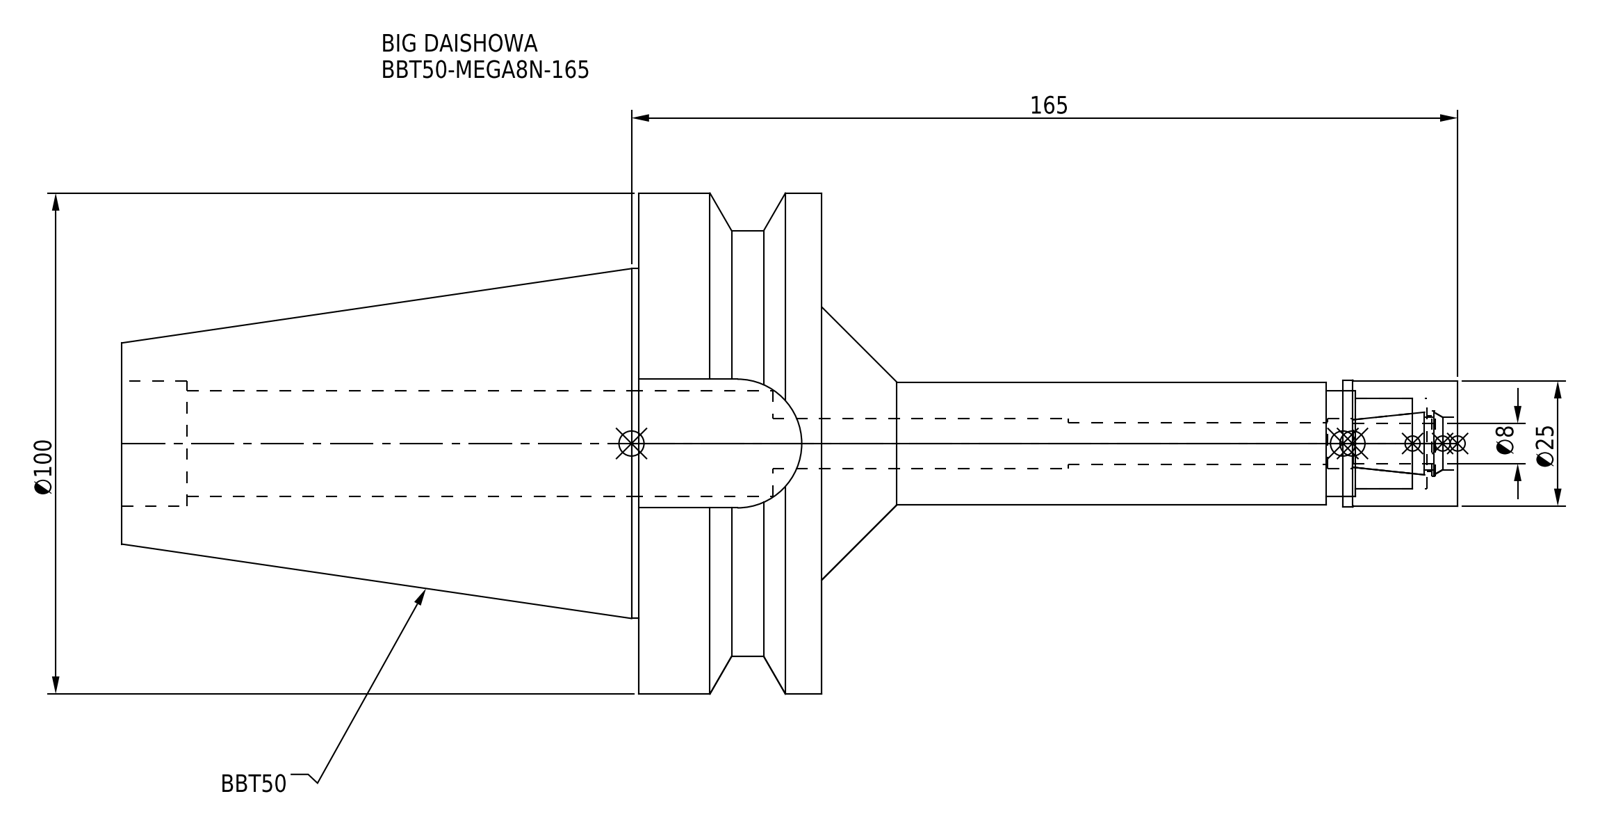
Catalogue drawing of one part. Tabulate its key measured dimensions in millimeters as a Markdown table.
| quantity | value |
| --- | --- |
| part name | BBT50-MEGA8N-165; MGN8_1.stp; BBT50-MEGA8N-165_1.stp; DXF_TEMP_ASSY_ASM_4_ASM.stp (+3 more) |
| STEP written by | SolidWorks 2019 (CONFIG_CONTROL_DESIGN) |
| units | millimeters |
| bodies | 2 solids, 79 faces (23 planar, 42 cylindrical, 14 other) |
| overall size | 266.8 × 100 × 100 |
| volume | 513 119 mm³ |
| surface area | 70 082 mm² |
| round holes (diameter × count) | 8.4 × 1, 10 × 1, 10.5 × 1, 11 × 1, 13 × 1, 18 × 1, 21 × 1, 21.2 × 1, 25 × 1 |
| round bosses / shafts (diameter × count) | 100 × 1, 85 × 1, 69.85 × 1, 25.3 × 1, 24.5 × 1 |
| partial cylindrical surfaces (radius × count) | 12.85 × 1 |
| main face-to-face distances | 36.5, 139.8, 103.3, 70.8, 25.7, 127, 163.5, 266.8, 136.8, 9.8 |
